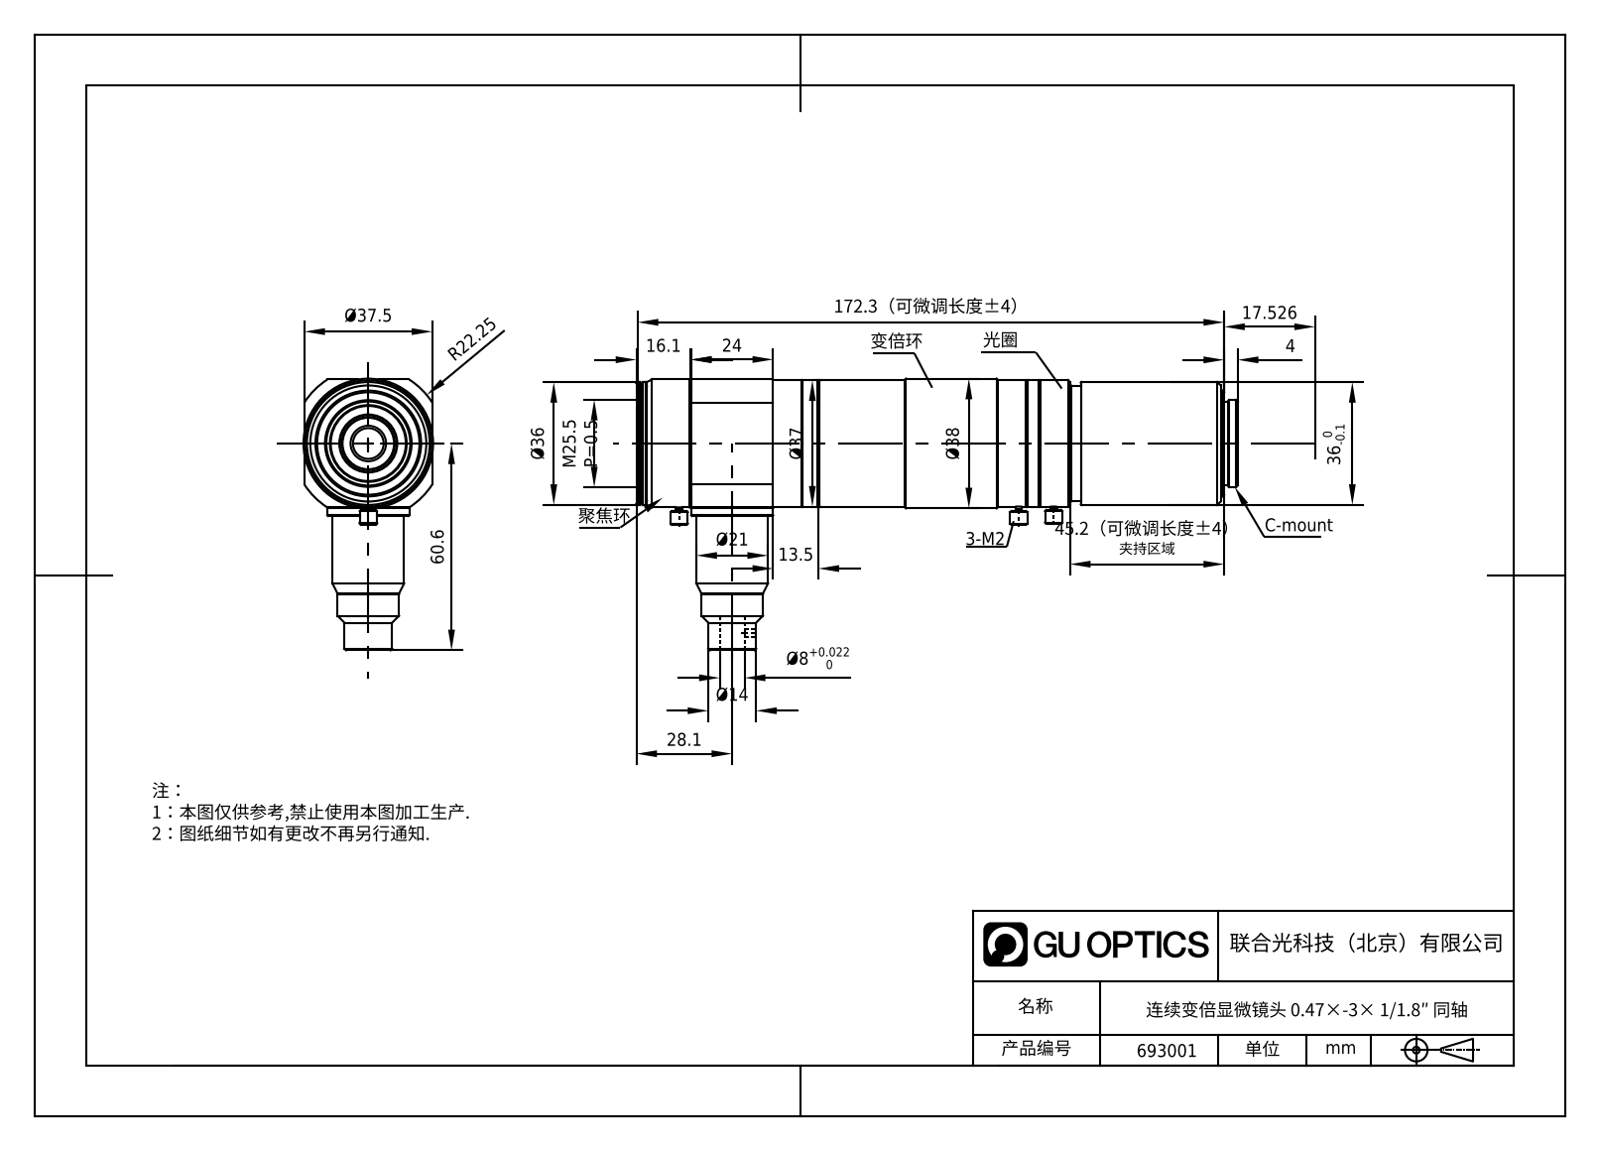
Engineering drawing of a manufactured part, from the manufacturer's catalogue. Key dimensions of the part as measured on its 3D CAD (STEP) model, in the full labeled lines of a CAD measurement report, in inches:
Part name (STEP PRODUCT): VSZ-0530CO
STEP written by: SolidWorks 2015 (CONFIG_CONTROL_DESIGN)
Units: inches
Bodies: 1 solid, 304 faces (50 planar, 94 cylindrical, 160 other)
Overall size (bounding box): 6.941 × 3.134 × 1.496
Volume: 11.18 in³ · Surface area: 52.99 in²
Round holes (diameter × count): ⌀0.354 ×1, ⌀0.787 ×1, ⌀0.866 ×1, ⌀0.965 ×1, ⌀0.984 ×1, ⌀1.004 ×1, ⌀1.083 ×1, ⌀1.102 ×1, ⌀1.181 ×1, ⌀1.319 ×1, ⌀1.339 ×1
Round bosses / shafts (diameter × count): ⌀0.197 ×3, ⌀0.079 ×3, ⌀0.063 ×3, ⌀1.496 ×1, ⌀1.476 ×1, ⌀1.457 ×1, ⌀1.417 ×1, ⌀1.378 ×1
Partial cylindrical surfaces — rounded edges, fillets, slot ends (radius × count): R0.876 ×1
Main face-to-face distances: 1.476, 0.354, 1.779, 5.291, 1.492, 3.799, 6.696, 5.204, 1.405, 6.342
